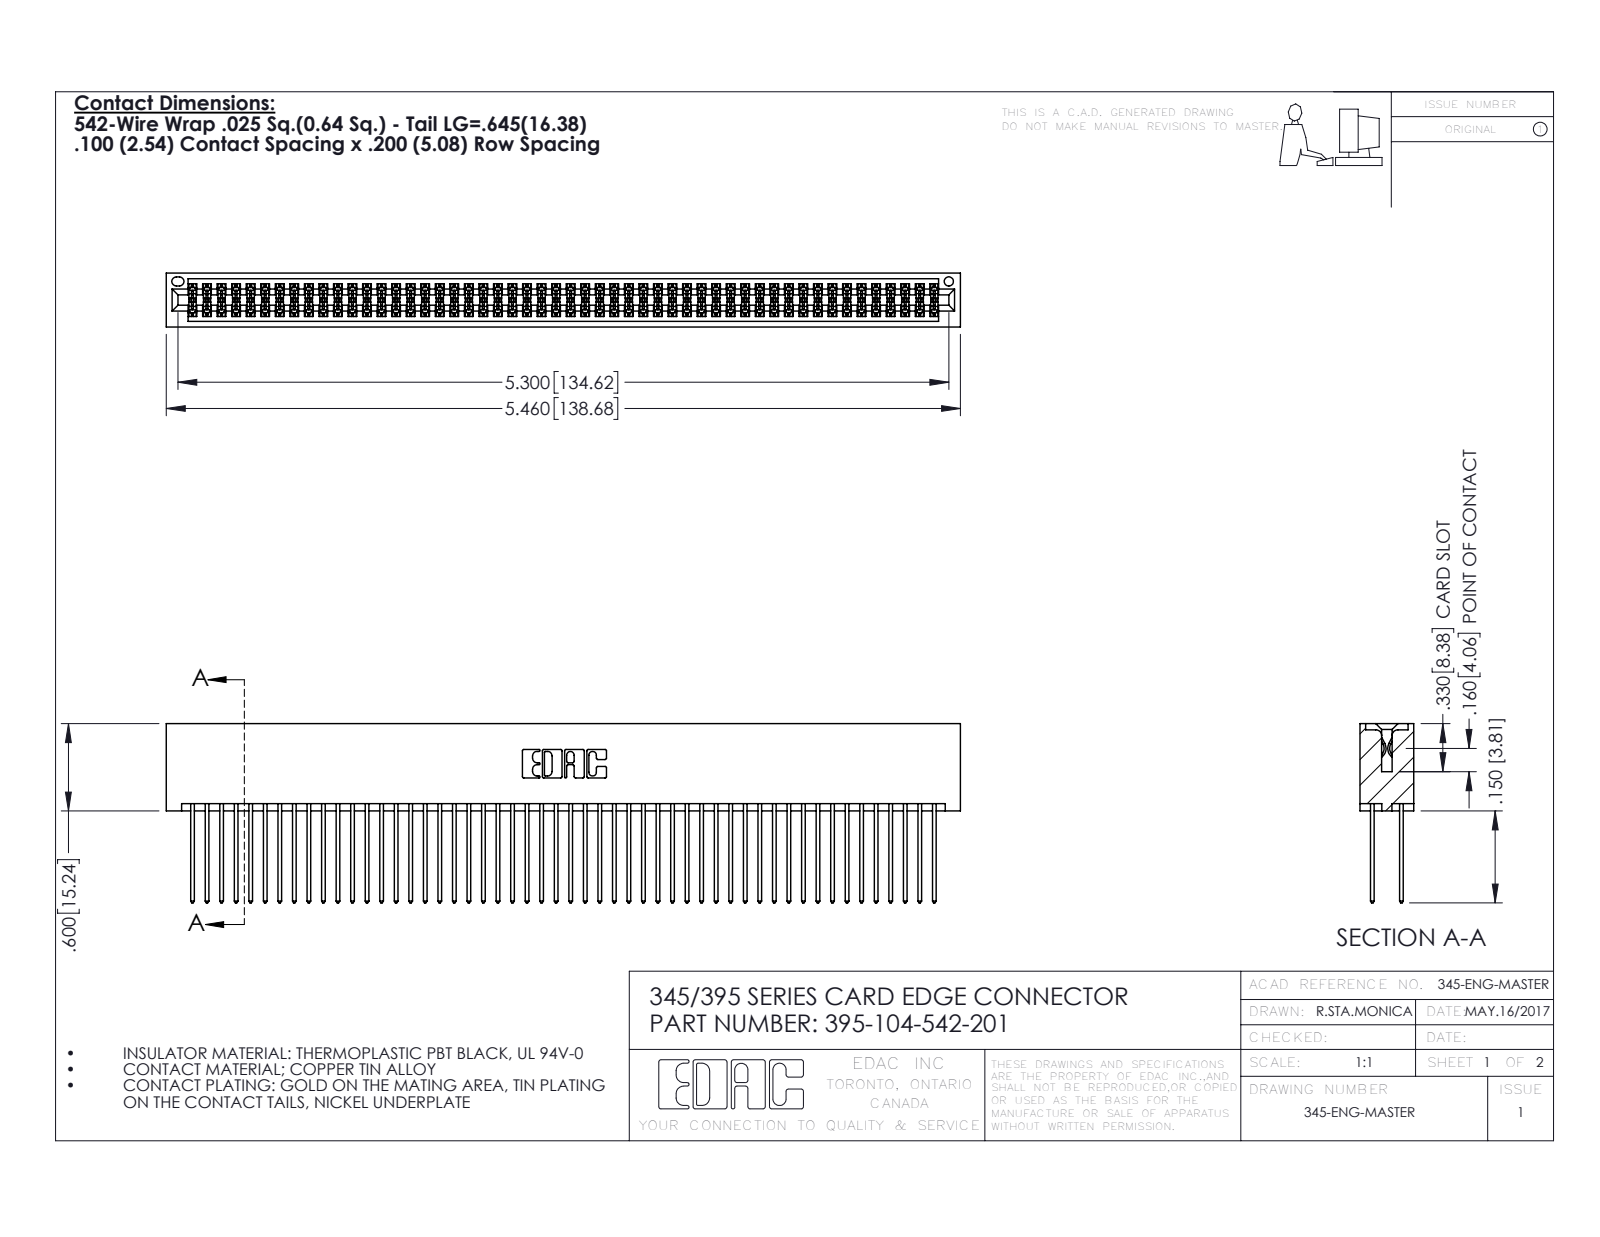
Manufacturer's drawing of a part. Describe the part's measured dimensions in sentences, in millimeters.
The part is named "345-292-001_345-293-142; 345 Part_No Mounting Lugs; 395-104-542-201". Its 3-D file was written by "SolidWorks 2016 (CONFIG_CONTROL_DESIGN)". It is 105 solids with 5318 faces: 3508 planar, 1810 cylindrical and 0 other. Overall it measures 138.7 by 31.3 by 9.4 millimeters. Its volume is 14 700 cubic millimeters and its surface area 24 440 square millimeters. Round holes: 1 of diameter 1.6. Partial cylindrical surfaces (rounded edges, fillets, slot ends): 156 of radius 0.2, 104 of radius 0.3, 22 of radius 0.3, 6 of radius 0.2, 6 of radius 0.8, 3 of radius 0.7, 2 of radius 0.4, 2 of radius 0.5. The main face-to-face distances are 7.6, 1.8, 5.1, 2.5, 6.9, 0.6, 5.7, 9.4, 4.4, 3.8.
